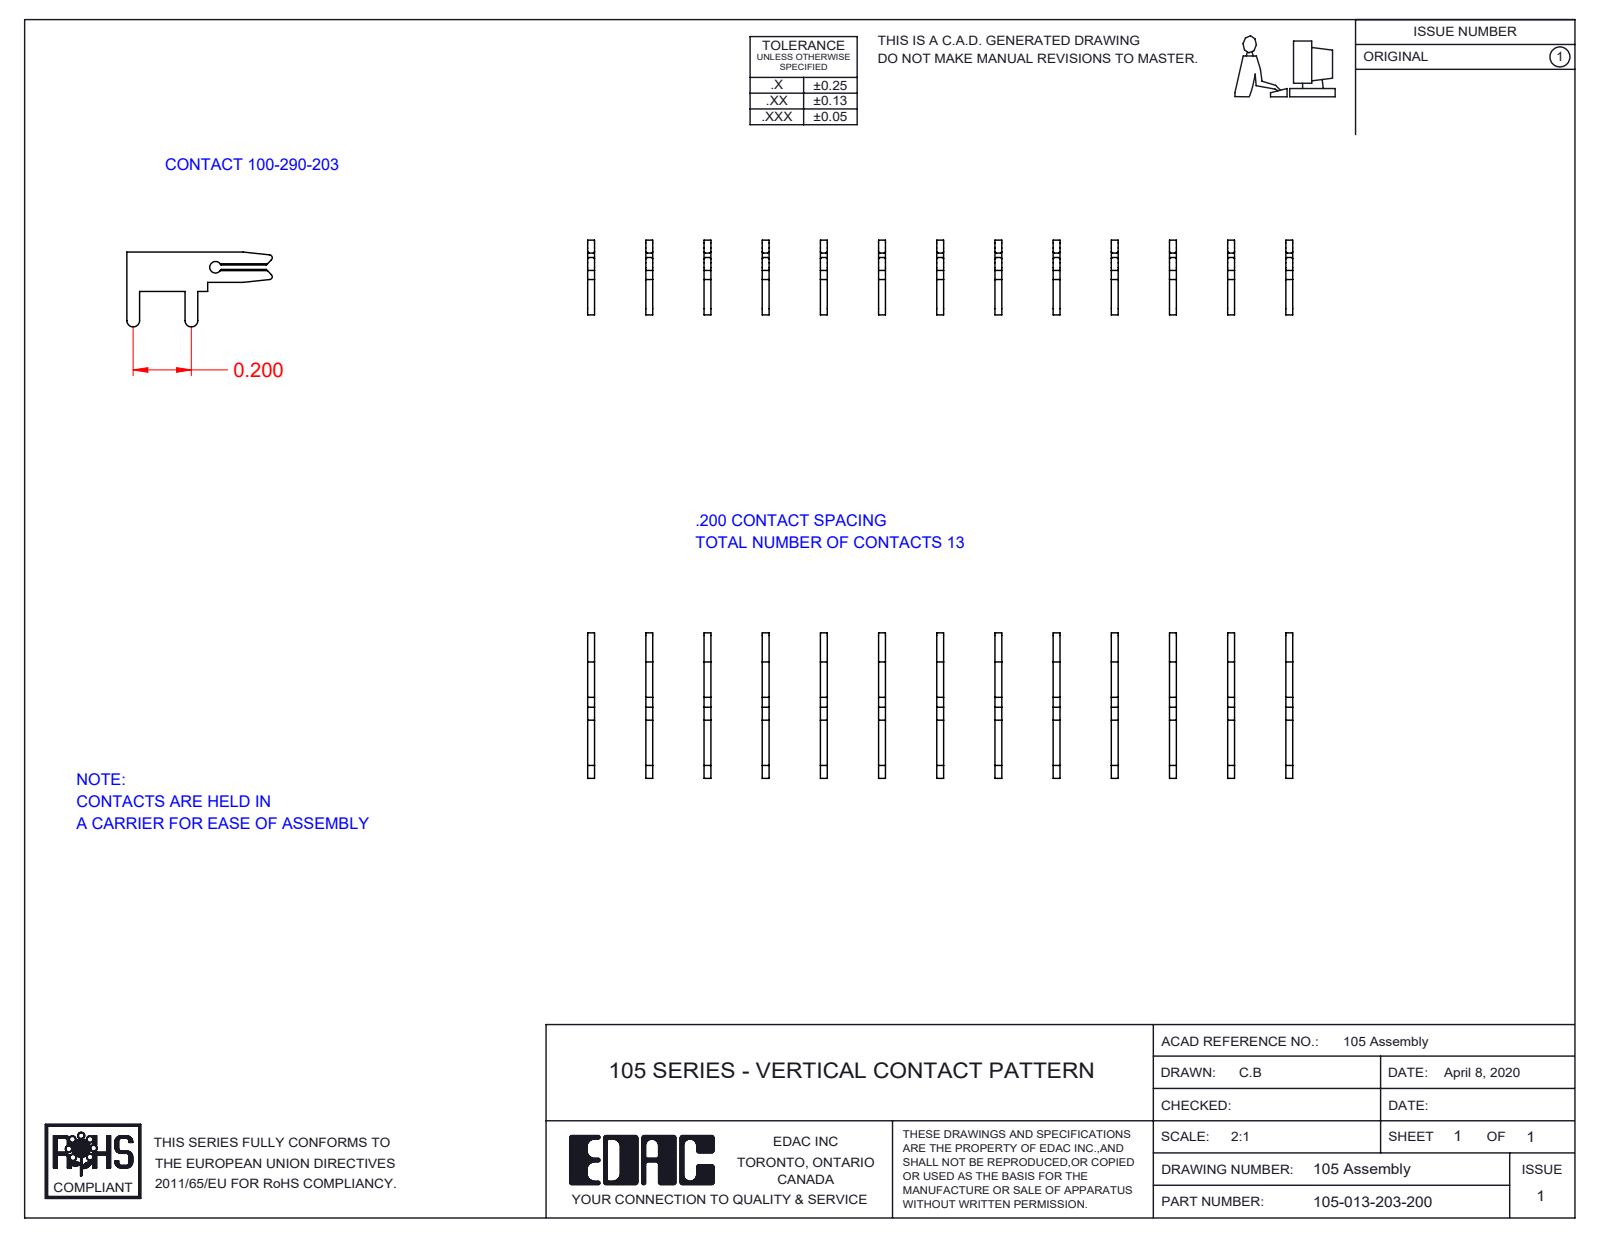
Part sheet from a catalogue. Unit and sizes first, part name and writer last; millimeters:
Units: millimetres
Overall size (bounding box): 61.6 × 12.7 × 6.5
Round holes (diameter × count): ⌀1 ×1
Partial cylindrical surfaces — rounded edges, fillets, slot ends (radius × count): R0.3 ×2, R0.6 ×2
Main face-to-face distances: 5.1, 10.2, 15.2, 20.3, 25.4, 30.5, 0.6, 5.7, 10.8, 15.8
Volume: 330 mm³ · Surface area: 1 505 mm²
Bodies: 13 solids, 364 faces (273 planar, 91 cylindrical, 0 other)
Part name (STEP PRODUCT): 100-290-001_100-290-203; 105-013-203-200
STEP written by: SolidWorks 2020 (CONFIG_CONTROL_DESIGN)
